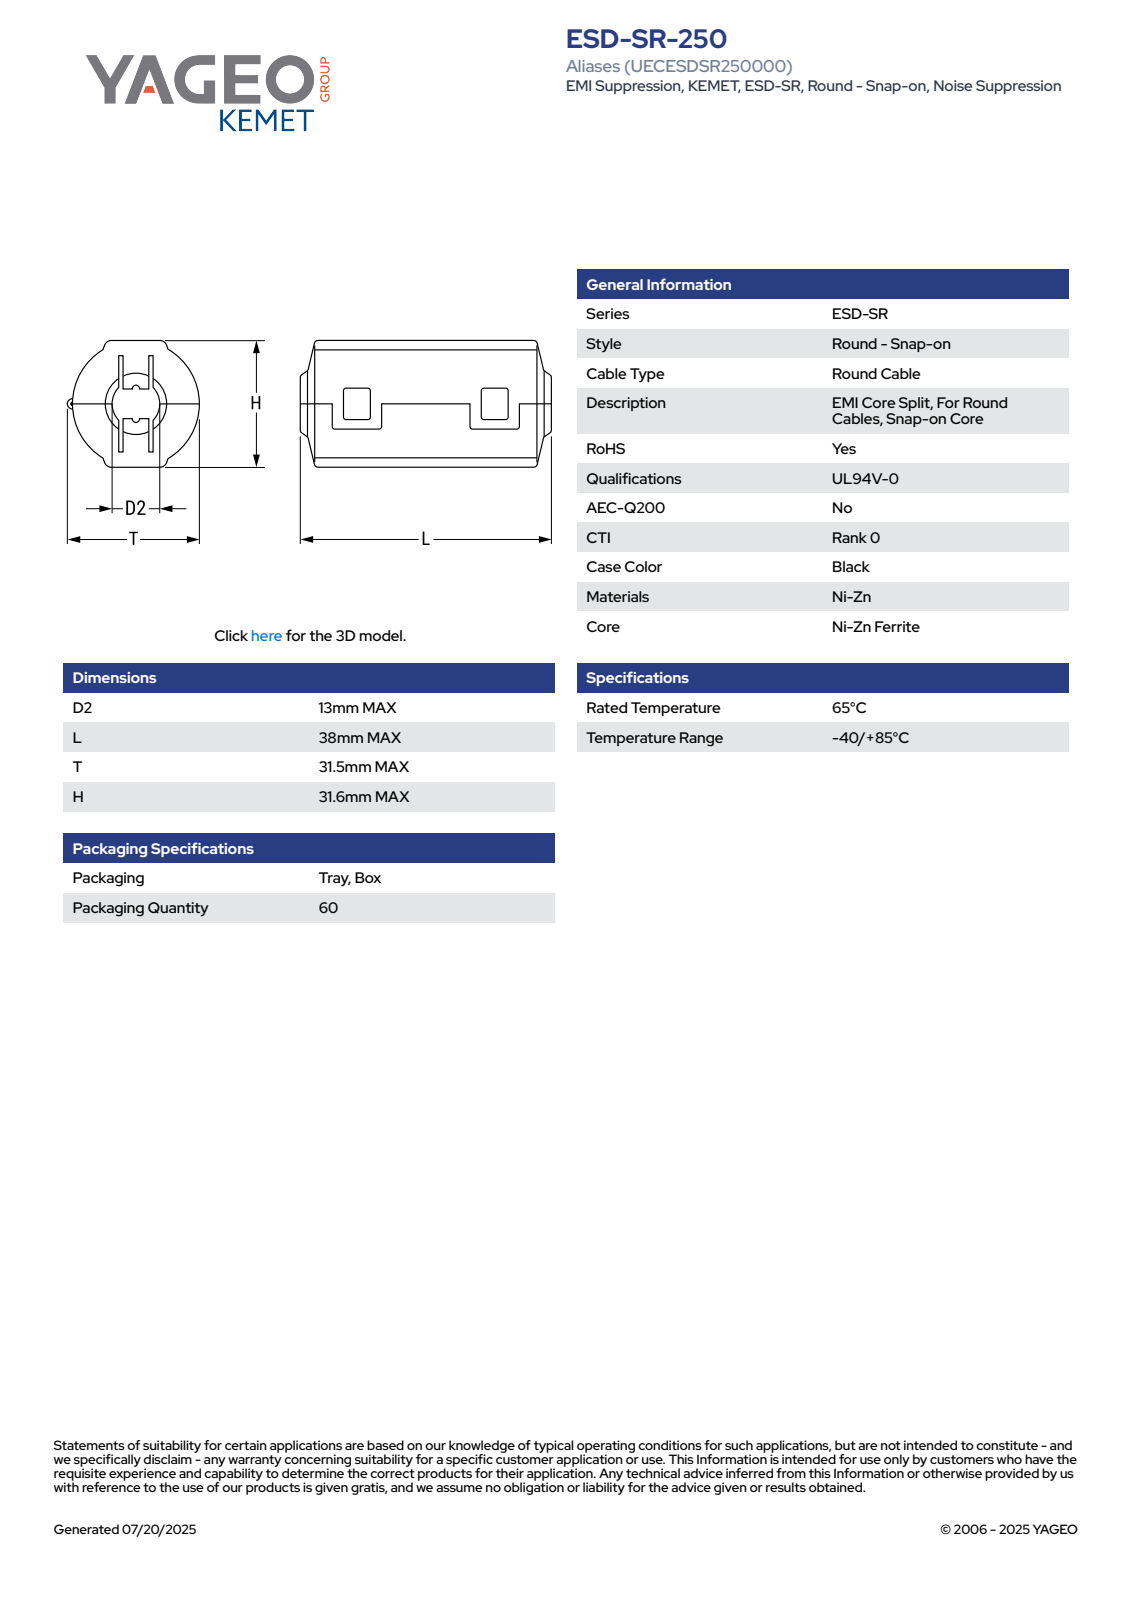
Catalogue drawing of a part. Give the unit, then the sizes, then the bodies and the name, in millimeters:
Units: millimetres
Overall size (bounding box): 38 × 31.61 × 31.5
Partial cylindrical surfaces — rounded edges, fillets, slot ends (radius × count): R5.57 ×2, R15.75 ×1
Main face-to-face distances: 11.8, 19.8, 31.6, 8, 2.25, 35.75, 38, 11.41, 33.5, 4.2
Volume: 24 593 mm³ · Surface area: 6 288 mm²
Bodies: 1 solid, 80 faces (66 planar, 6 cylindrical, 8 other)
Part name (STEP PRODUCT): EC_ESDSR_D213L38T31.5H31.6
STEP written by: SolidWorks 2014 (AUTOMOTIVE_DESIGN)
